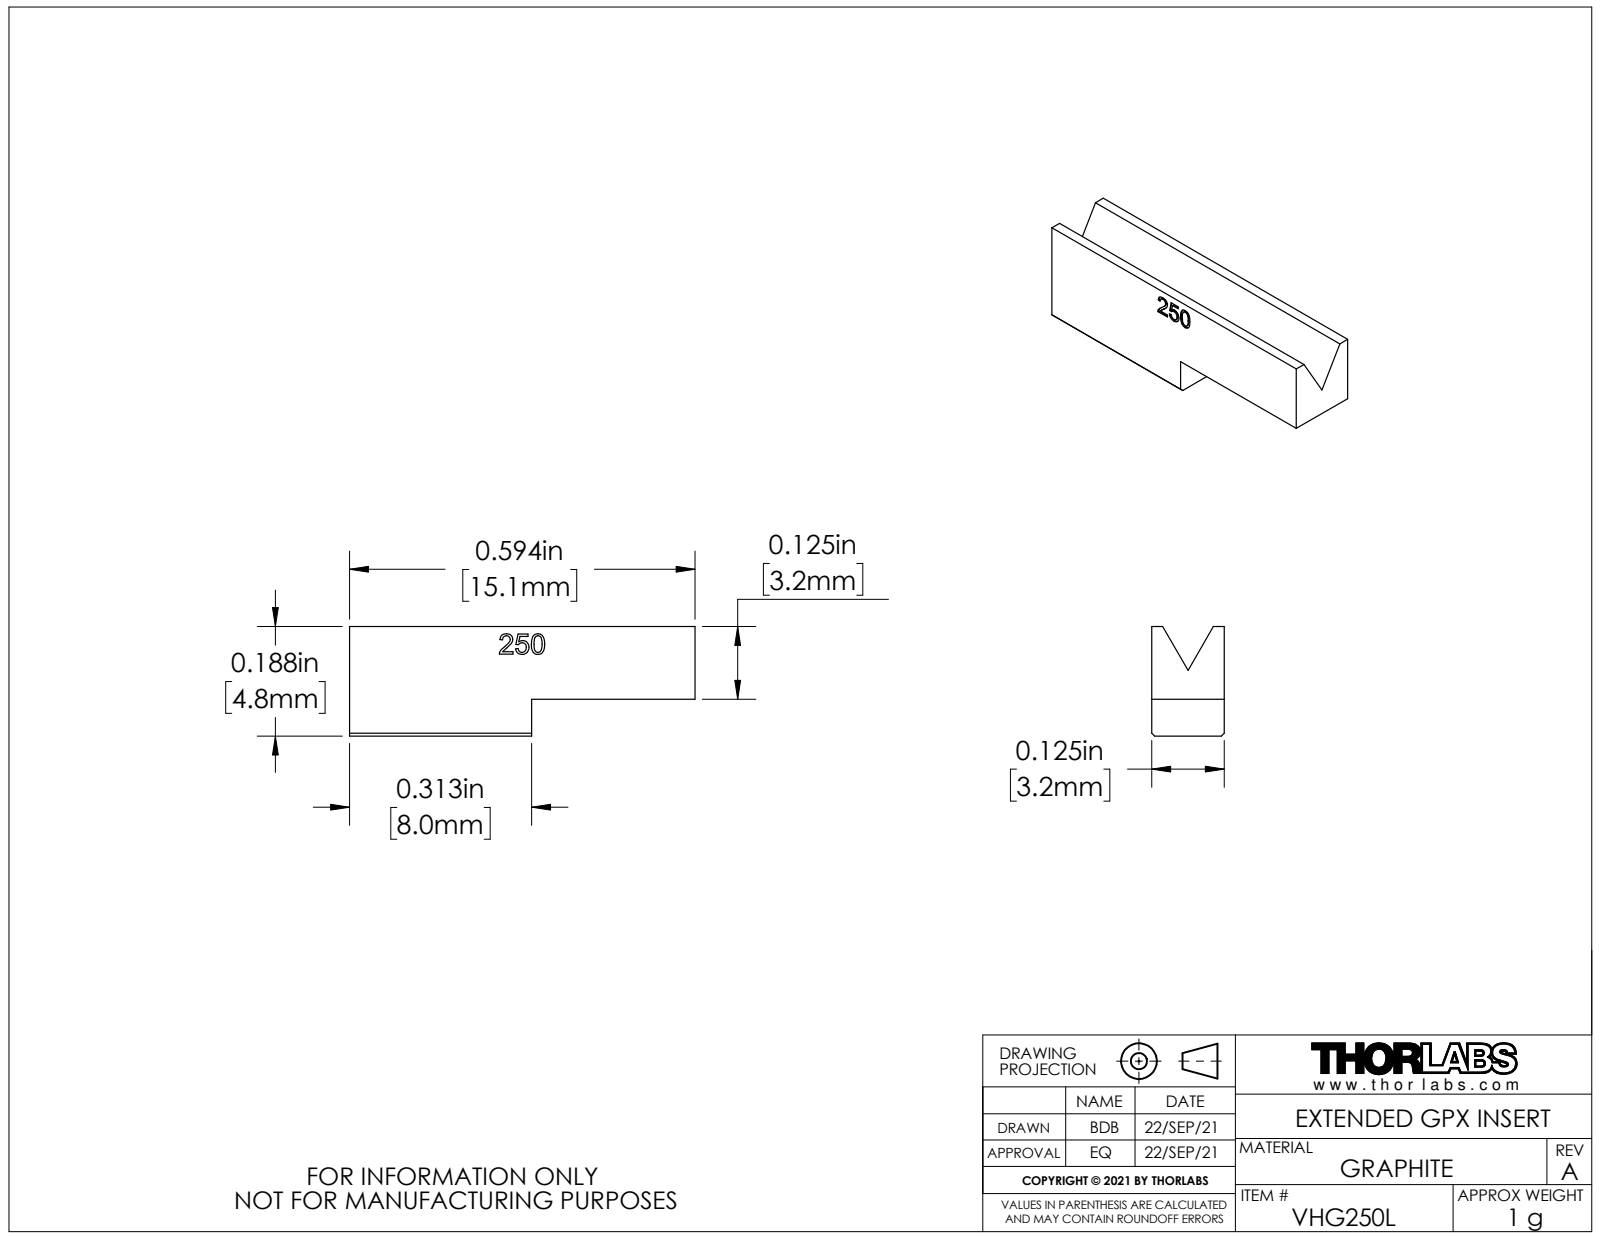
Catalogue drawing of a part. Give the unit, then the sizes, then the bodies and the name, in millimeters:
Units: millimetres
Overall size (bounding box): 15.1 × 4.8 × 3.2
Partial cylindrical surfaces — rounded edges, fillets, slot ends (radius × count): R0.4 ×2
Main face-to-face distances: 3.1, 1.2, 2, 1.6, 4.8, 3.2, 0.8, 15.1, 8, 7.1
Volume: 100 mm³ · Surface area: 310 mm²
Bodies: 1 solid, 105 faces (47 planar, 2 cylindrical, 56 other)
Part name (STEP PRODUCT): TTN113920-E0W
STEP written by: SolidWorks 2018 (CONFIG_CONTROL_DESIGN)
